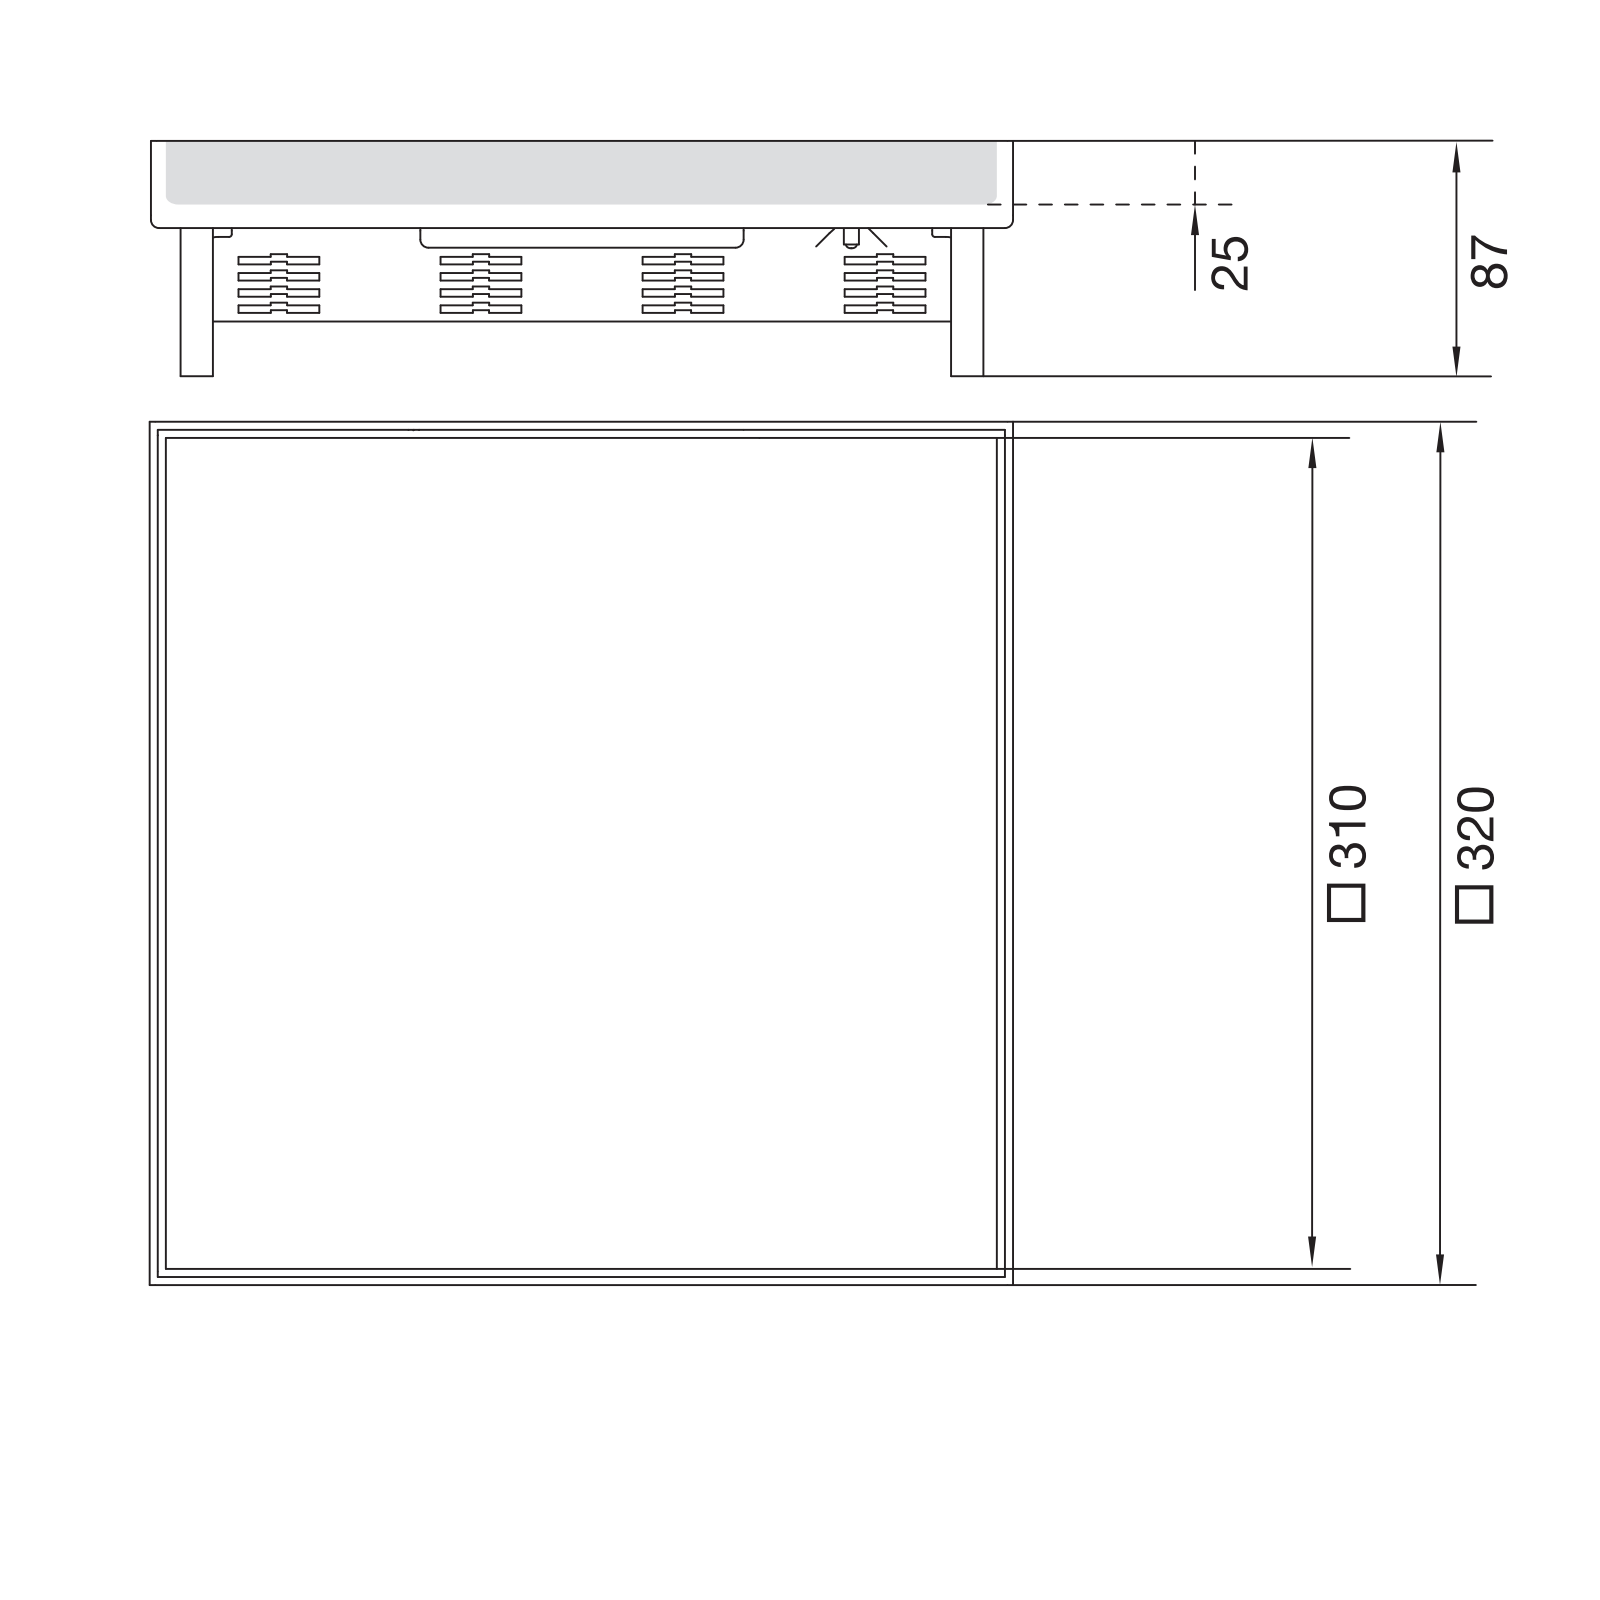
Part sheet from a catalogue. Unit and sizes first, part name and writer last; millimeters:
Units: millimetres
Overall size (bounding box): 320 × 320 × 87
Round bosses / shafts (diameter × count): ⌀12 ×4, ⌀9.85 ×4
Partial cylindrical surfaces — rounded edges, fillets, slot ends (radius × count): R1 ×10, R3 ×10, R10 ×6, R5 ×2
Main face-to-face distances: 2, 3, 5, 315, 318, 45.3, 272.7, 1, 317, 42.3
Volume: 425 524 mm³ · Surface area: 444 897 mm²
Bodies: 2 solids, 188 faces (136 planar, 52 cylindrical, 0 other)
Part name (STEP PRODUCT): T-00645; U09001; T-00834_ASM; T-00650 (+2 more)
STEP written by: CREO PARAMETRIC BY PTC INC, 2022024 (AUTOMOTIVE_DESIGN)
